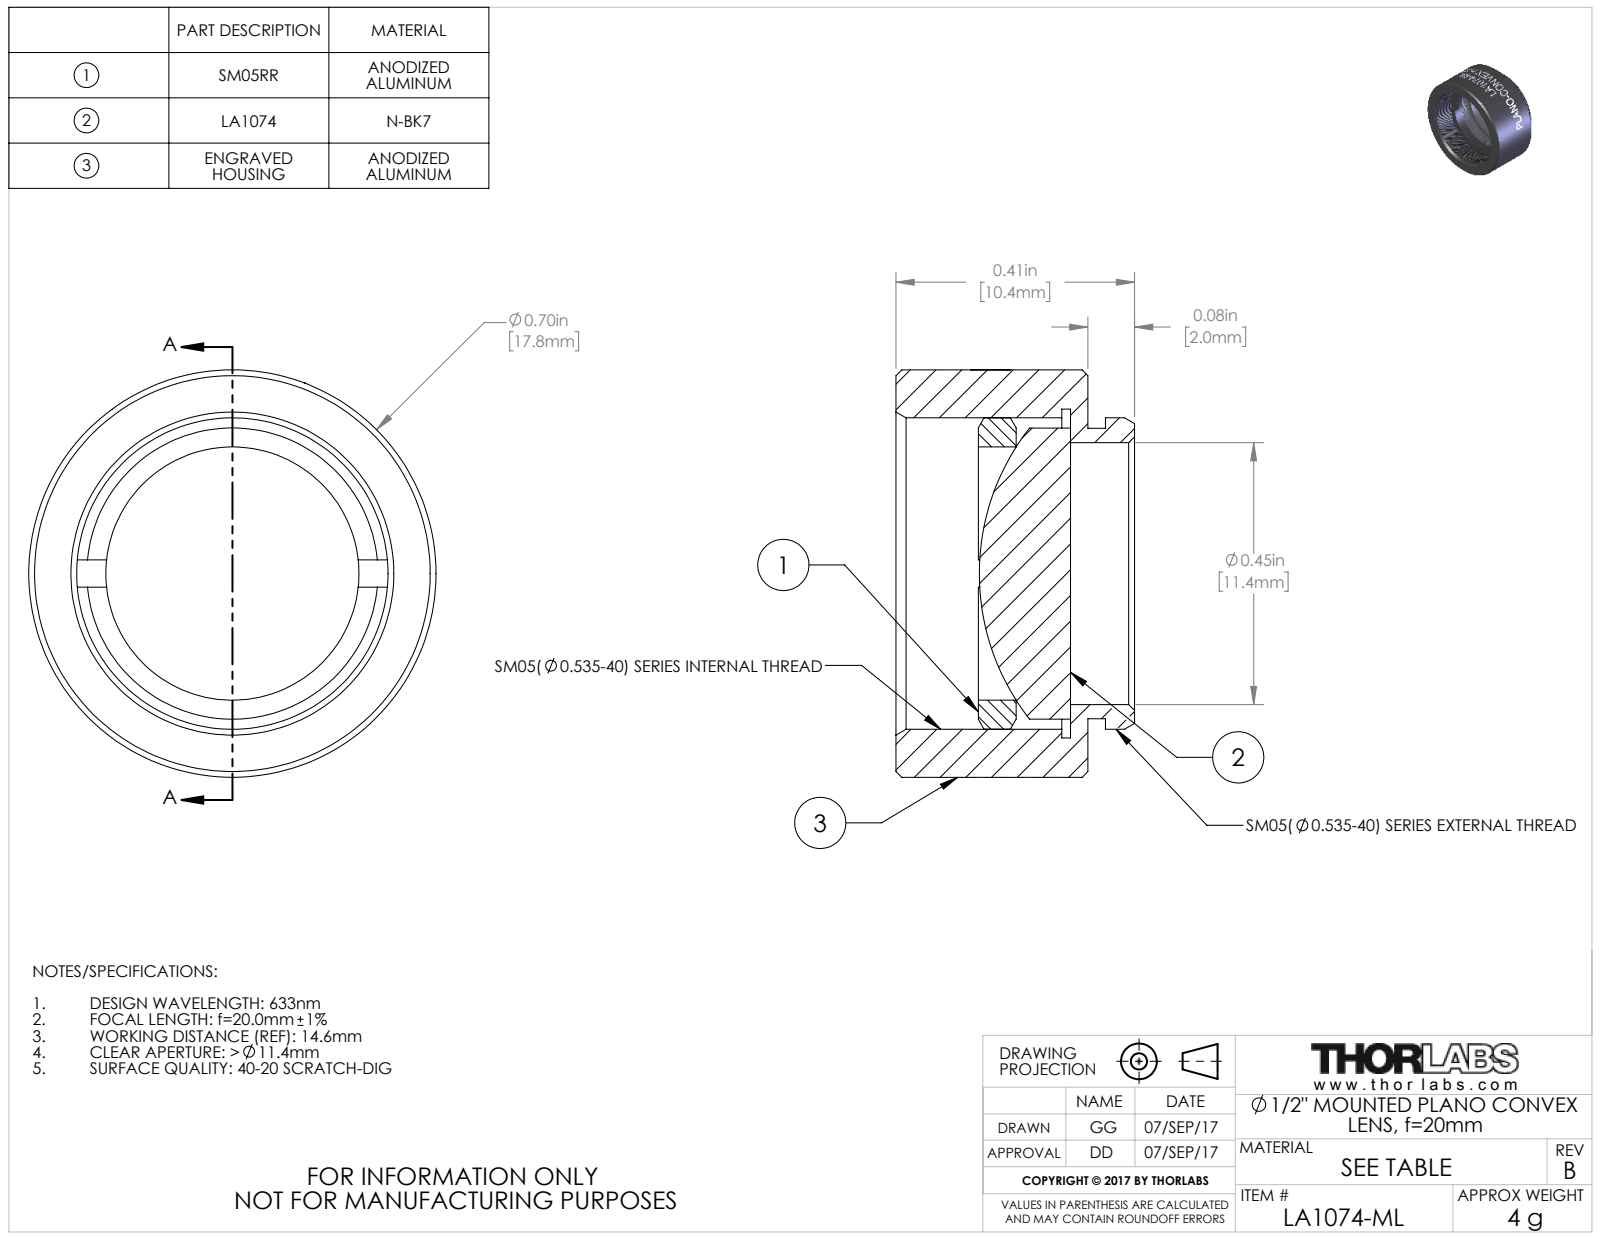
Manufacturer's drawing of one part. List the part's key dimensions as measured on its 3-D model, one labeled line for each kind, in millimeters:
Part name (STEP PRODUCT): 24390-E0W
STEP written by: SolidWorks 2016 (CONFIG_CONTROL_DESIGN)
Units: millimetres
Bodies: 3 solids, 242 faces (94 planar, 73 cylindrical, 75 other)
Overall size (bounding box): 17.8 × 17.8 × 10.4
Volume: 1 400 mm³ · Surface area: 1 854 mm²
Round holes (diameter × count): ⌀11 ×1, ⌀11.4 ×1, ⌀13.6 ×1, ⌀14.4 ×1
Round bosses / shafts (diameter × count): ⌀17.8 ×1, ⌀13.6 ×1, ⌀12.7 ×1, ⌀12.7 ×1
Partial cylindrical surfaces — rounded edges, fillets, slot ends (radius × count): R8.9 ×1
Main face-to-face distances: 0.8, 7.6, 8.4, 3.1, 2.4, 5.3, 4, 4.8, 1.7, 3.6
